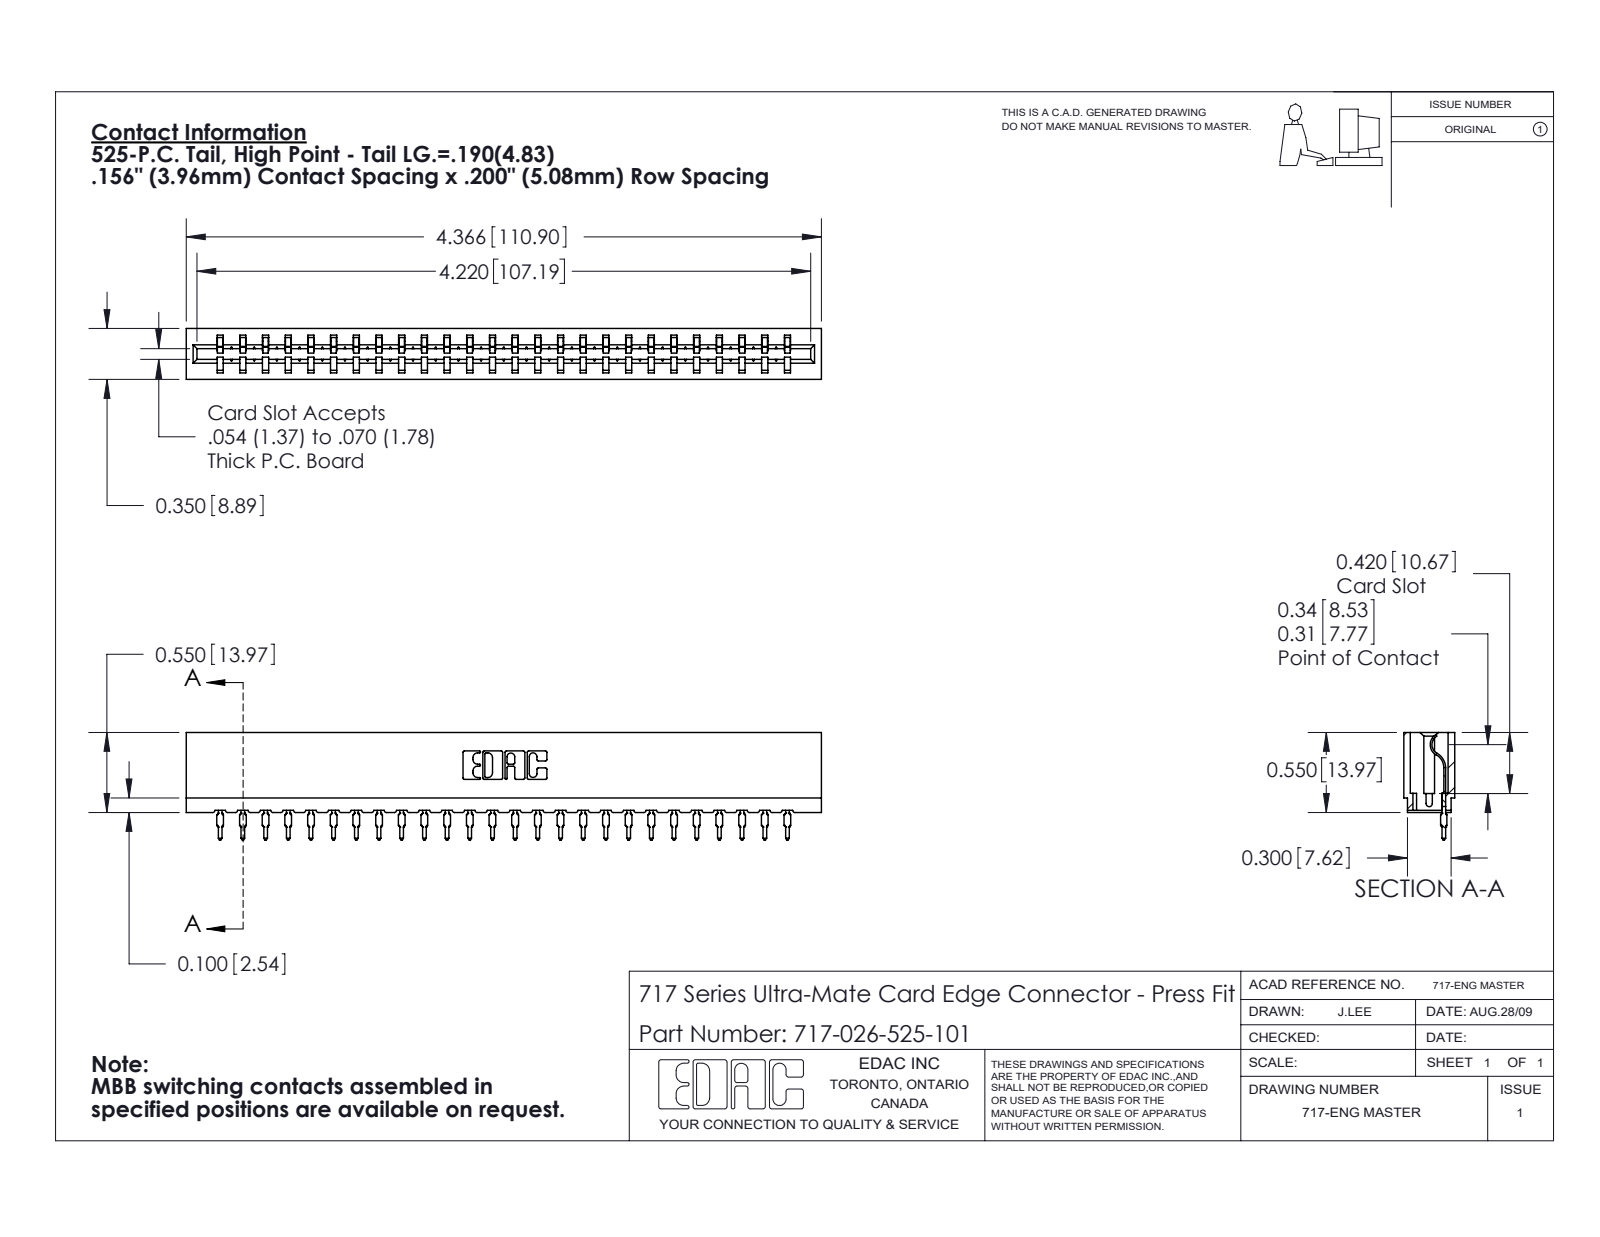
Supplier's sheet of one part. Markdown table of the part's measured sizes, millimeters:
| quantity | value |
| --- | --- |
| part name | 717 Part_Insulator Option - 06; 717-026-525-101; 745-292-001_525 |
| STEP written by | SolidWorks 2020 (CONFIG_CONTROL_DESIGN) |
| units | millimeters |
| bodies | 27 solids, 3032 faces (1822 planar, 534 cylindrical, 676 other) |
| overall size | 110.9 × 18.8 × 8.9 |
| volume | 9 410 mm³ |
| surface area | 12 970 mm² |
| partial cylindrical surfaces (radius × count) | 0.4 × 52, 0.5 × 52, 0.3 × 22, 0.2 × 6, 0.8 × 6, 0.1 × 4, 0.3 × 4, 0.7 × 3 |
| main face-to-face distances | 5.4, 3.5, 8.9, 4, 1.9, 1.1, 7.7, 2.4, 4.2, 0.6 |
